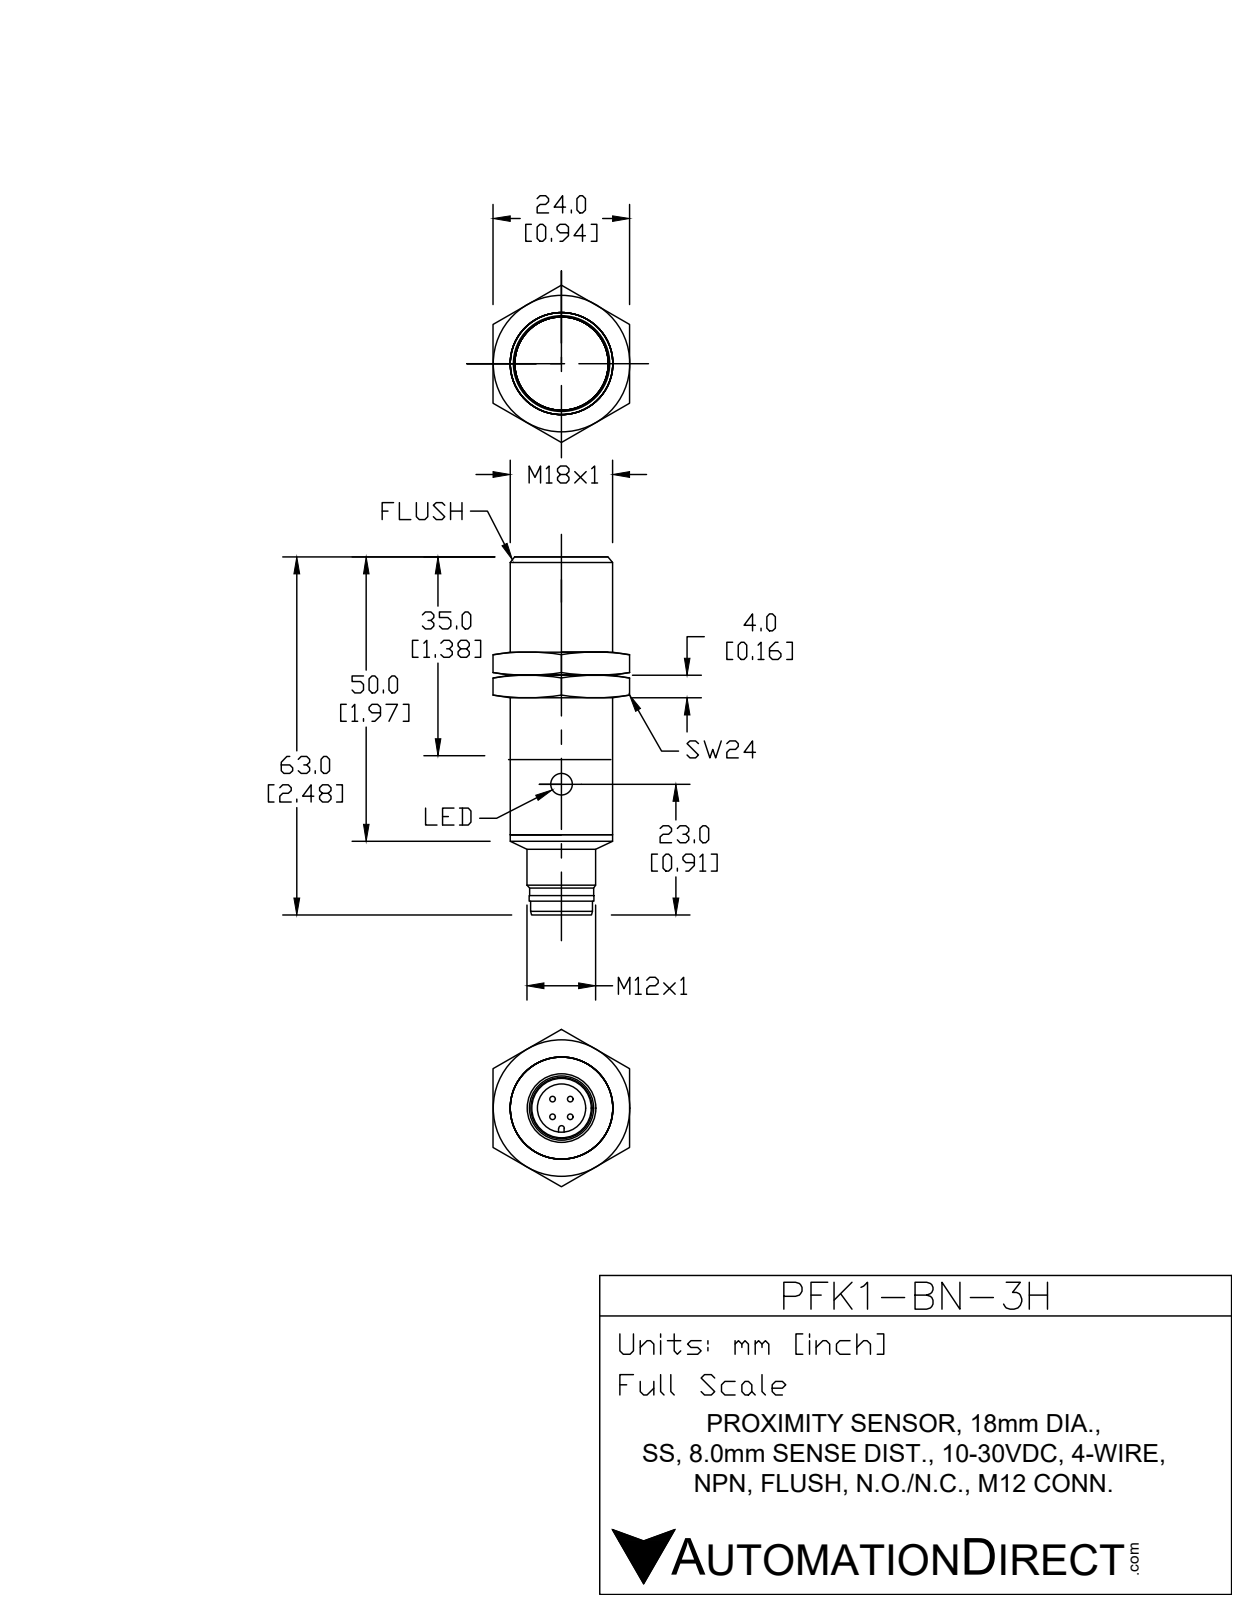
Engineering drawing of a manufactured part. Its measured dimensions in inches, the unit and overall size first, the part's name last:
Units: inches
Overall size (bounding box): 2.484 × 0.709 × 0.709
Round holes (diameter × count): ⌀0.157 ×1, ⌀0.331 ×1, ⌀0.335 ×1, ⌀0.374 ×1, ⌀0.622 ×1
Round bosses / shafts (diameter × count): ⌀0.039 ×4, ⌀0.709 ×1, ⌀0.472 ×1, ⌀0.413 ×1, ⌀0.37 ×1
Partial cylindrical surfaces — rounded edges, fillets, slot ends (radius × count): R0.024 ×1, R0.326 ×1
Main face-to-face distances: 1.539, 0.394, 1.933, 2.087, 1.693, 0.154, 2.134, 1.74, 0.201, 0.047
Volume: 0.839 in³ · Surface area: 10.28 in²
Bodies: 4 solids, 69 faces (12 planar, 35 cylindrical, 22 other)
Part name (STEP PRODUCT): PFK1-BN-3H
STEP written by: SolidWorks 2017 (AUTOMOTIVE_DESIGN)
